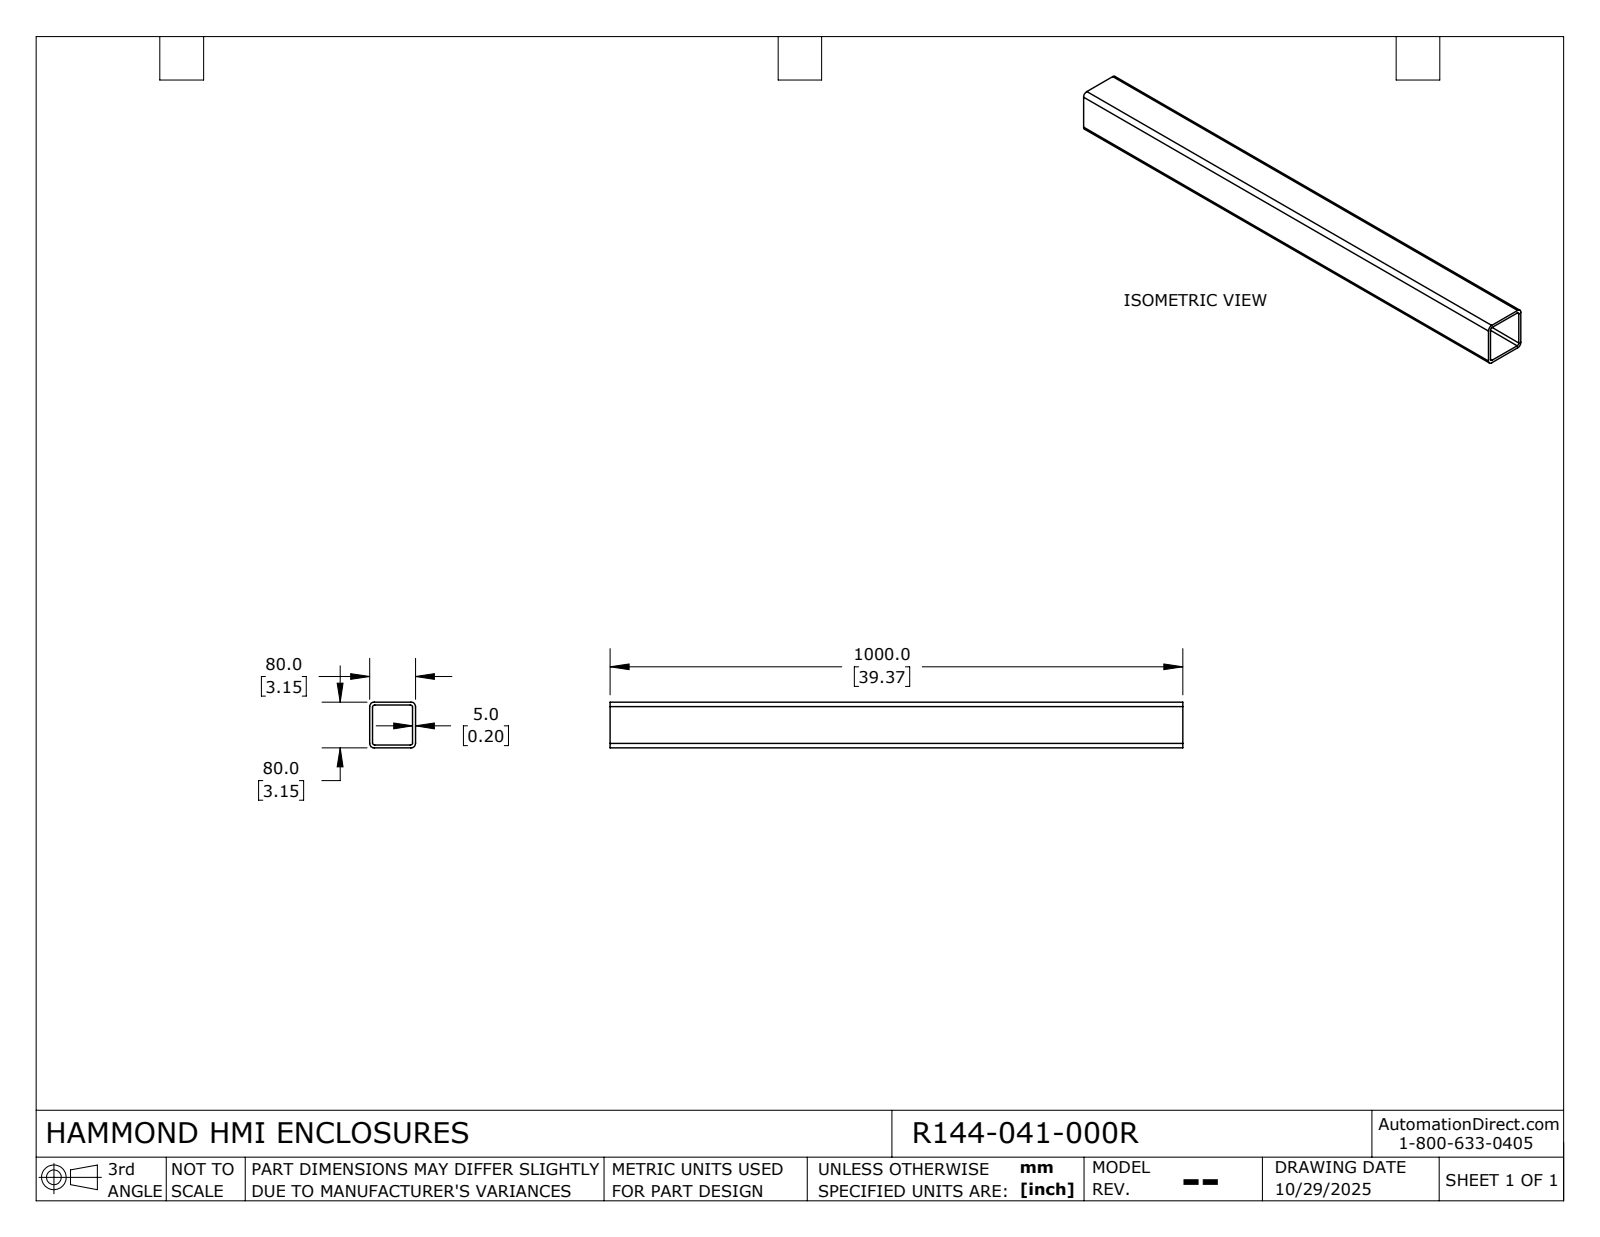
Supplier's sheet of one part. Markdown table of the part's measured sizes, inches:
| quantity | value |
| --- | --- |
| part name | R144-041-000R |
| STEP written by | SolidWorks 2024 (AUTOMOTIVE_DESIGN) |
| units | inches |
| bodies | 1 solid, 18 faces (10 planar, 8 cylindrical, 0 other) |
| overall size | 39.37 × 3.15 × 3.15 |
| volume | 89.03 in³ |
| surface area | 902.6 in² |
| partial cylindrical surfaces (radius × count) | 0.157 × 4, 0.315 × 4 |
| main face-to-face distances | 0.197, 2.953, 3.15, 2.756, 39.37 |
